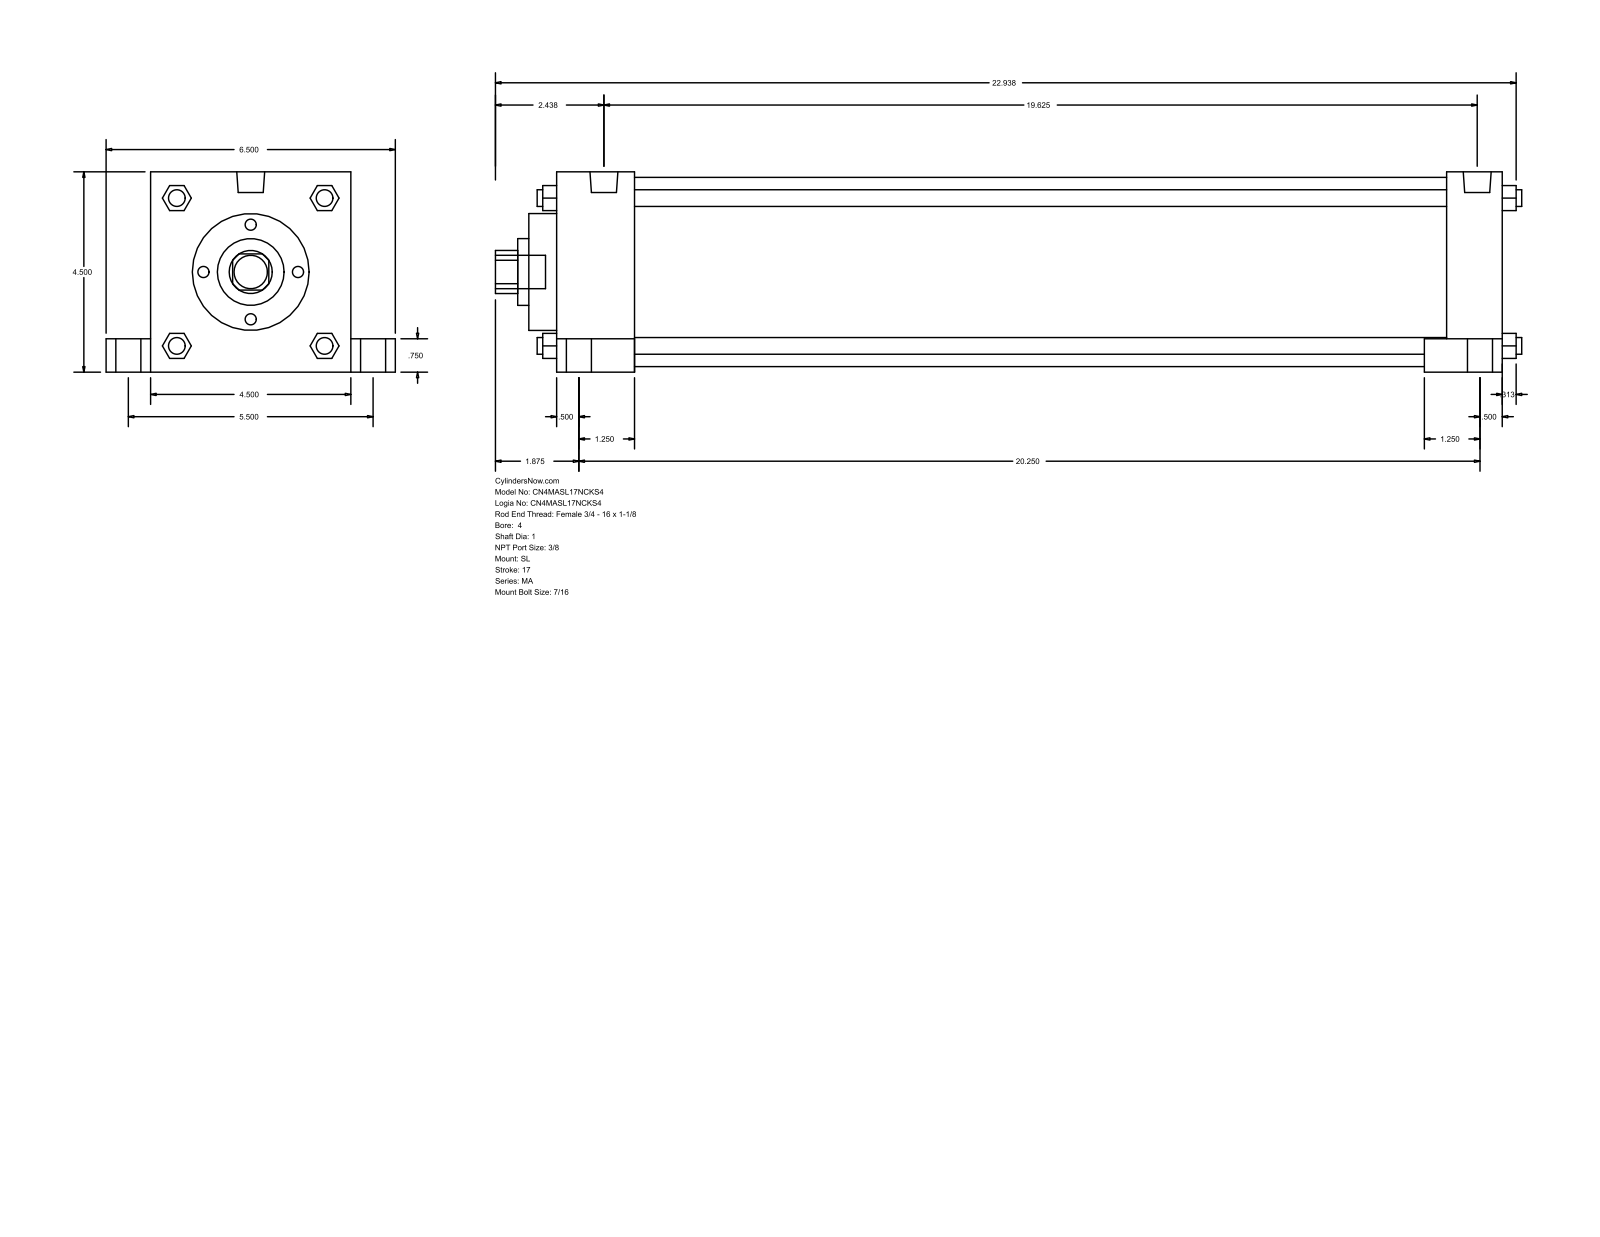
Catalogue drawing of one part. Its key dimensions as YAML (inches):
part_name: "MA_SL__0400_1"
step_written_by: "GSSL Pune (CONFIG_CONTROL_DESIGN)"
units: inches
bodies: {solids: 0, faces: 150, planar: 113, cylindrical: 37, other: 0}
overall_size: [23.063, 6.5, 4.5]
round_holes:
  - {diameter: 1, count: 1}
  - {diameter: 1.5, count: 1}
  - {diameter: 2.625, count: 1}
  - {diameter: 4.25, count: 1}
round_bosses_or_shafts:
  - {diameter: 0.813, count: 4}
  - {diameter: 0.563, count: 4}
  - {diameter: 0.437, count: 4}
  - {diameter: 0.375, count: 4}
  - {diameter: 0.627, count: 2}
  - {diameter: 0.75, count: 1}
partial_cylinders:
  - {radius: 0.484, count: 1}
face_to_face_distances: [4.5, 21.25, 1.75, 19.5, 20, 18.25, 1.25, 1, 5.5, 21.875]
